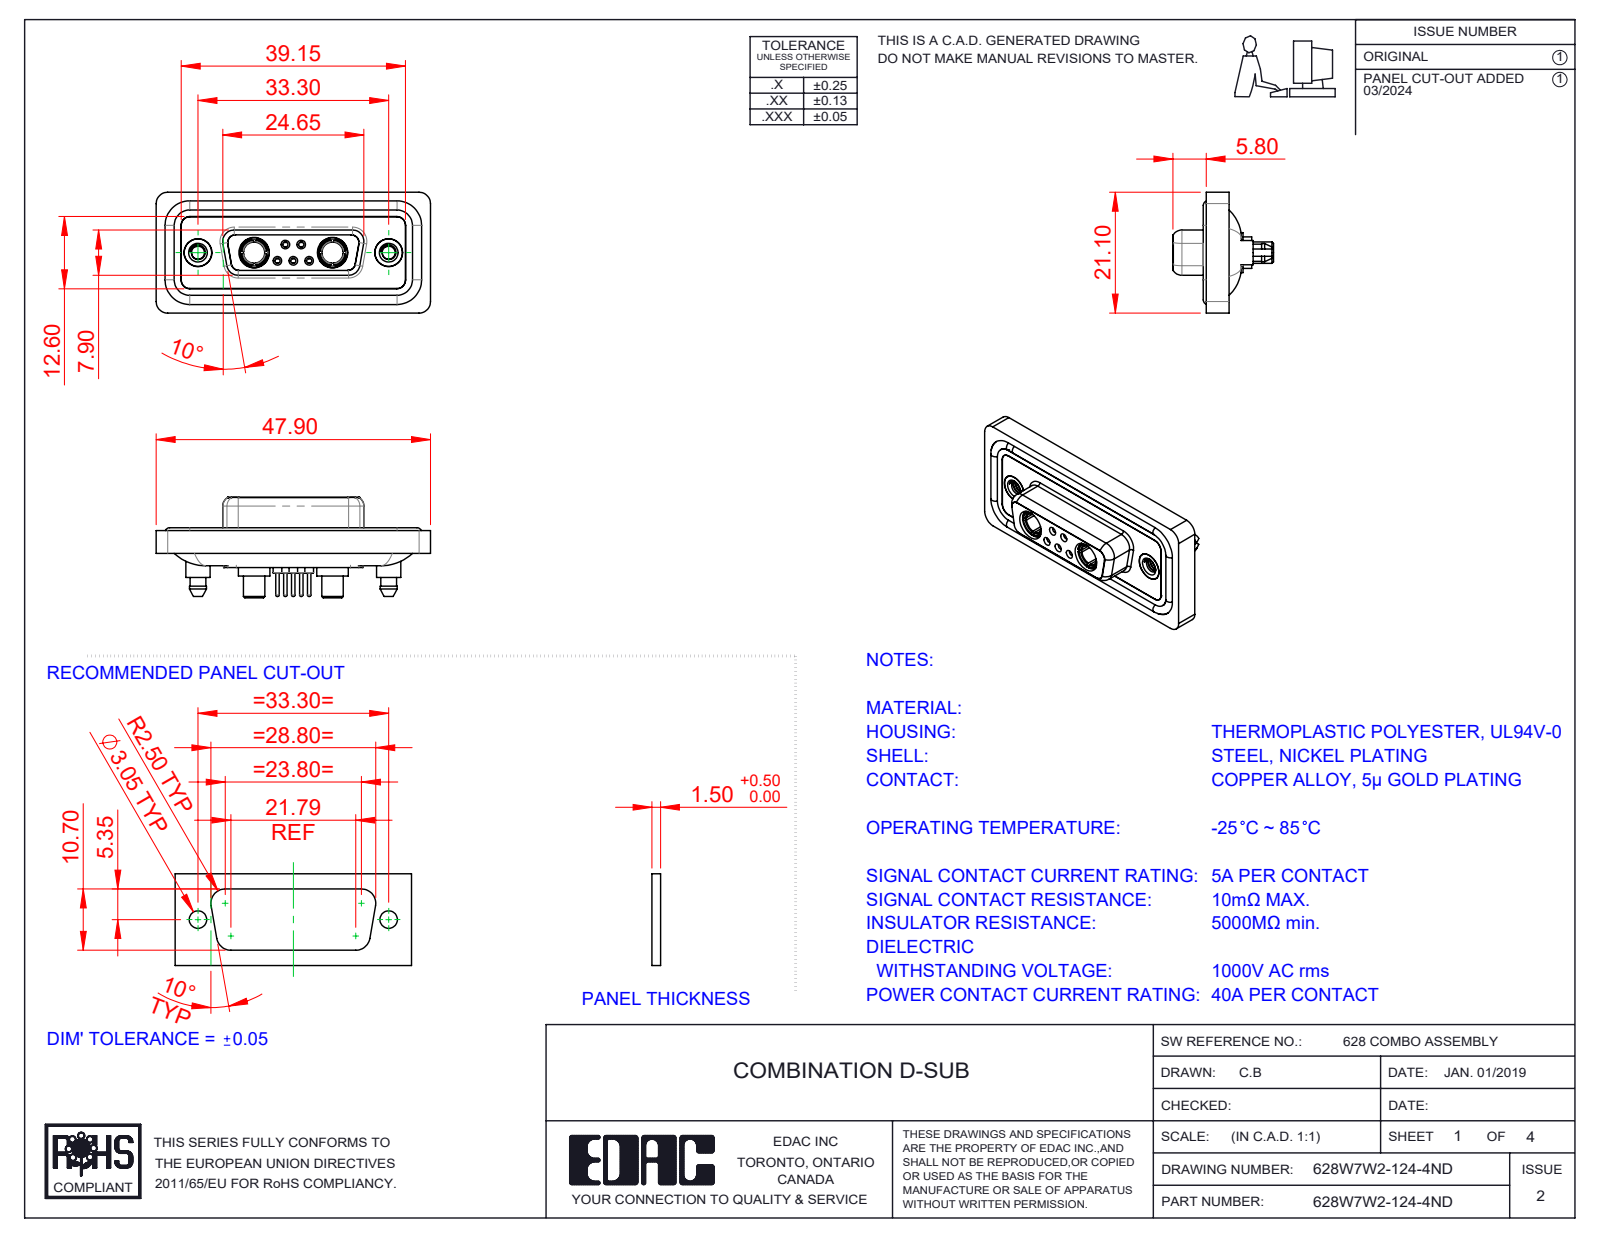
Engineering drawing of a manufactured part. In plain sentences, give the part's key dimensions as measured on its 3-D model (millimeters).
The part is named "628Combo Contact Row 2_24; 628Combo Housing_7W2; 628Combo Shell Front_15 Contacts; 628Combo Waterproof Housing_15 Contacts (+5 more)". Its 3-D file was written by "SolidWorks 2023 (CONFIG_CONTROL_DESIGN)". It is 16 solids with 875 faces: 254 planar, 377 cylindrical and 244 other. Overall it measures 47.9 by 21.1 by 17.55 millimeters. Its volume is 6 249 cubic millimeters and its surface area 10 246 square millimeters. Round holes: 5 of diameter 0.9, 5 of diameter 1.1, 5 of diameter 1.5, 5 of diameter 2, 4 of diameter 4.85, 3 of diameter 1.6, 2 of diameter 1.7, 2 of diameter 2.26, 2 of diameter 3.7, 2 of diameter 4, 2 of diameter 4.05, 2 of diameter 5. Round bosses or shafts: 6 of diameter 1.6, 5 of diameter 2.2, 5 of diameter 0.6, 2 of diameter 5.5, 2 of diameter 5.4, 2 of diameter 5.2, 2 of diameter 4.96, 2 of diameter 4.95. Partial cylindrical surfaces (rounded edges, fillets, slot ends): 24 of radius 1.5, 20 of radius 2, 12 of radius 1.35, 10 of radius 1.6, 4 of radius 0.25, 4 of radius 0.5, 4 of radius 0.6, 4 of radius 0.65. The main face-to-face distances are 0.4, 1.8, 1.6, 0.5, 2.9, 1.1, 7.45, 5.65, 6.6, 7.05. The hole center spacings are 3.16, 2.77, 9.8, 23.5, 4.31, 4.33, 5.03, 5.04.
